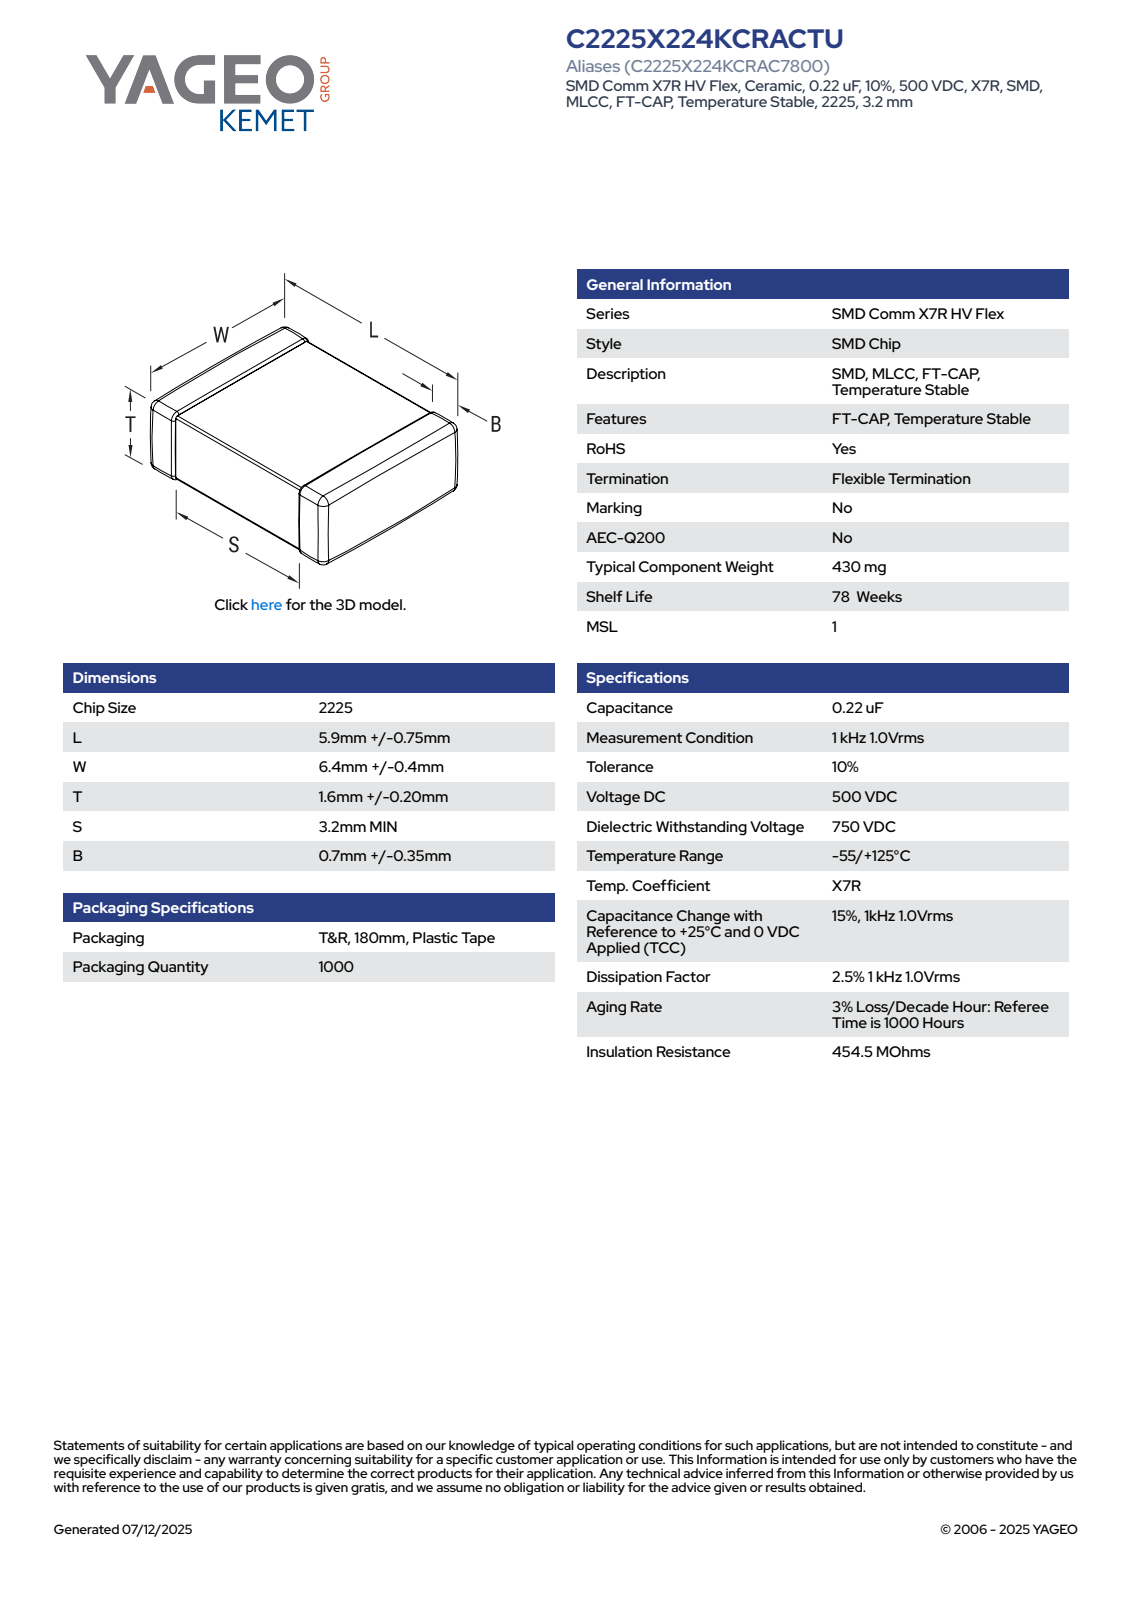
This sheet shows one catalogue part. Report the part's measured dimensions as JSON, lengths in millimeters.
{"part_name": "CCS_CCSTD_2225_L6.65W6.8T1.8B0.7", "step_written_by": "SolidWorks 2021 (AUTOMOTIVE_DESIGN)", "units": "millimeters", "bodies": {"solids": 4, "faces": 121, "planar": 71, "cylindrical": 34, "other": 16}, "overall_size": [6.8, 6.65, 1.8], "volume_mm3": 70, "surface_area_mm2": 139, "partial_cylinders_radius": [[0.14, 24]], "face_to_face_distances": [1.52, 1.66, 1.8, 6.65, 6.52, 6.66, 6.8, 1, 2.59, 4.06]}
